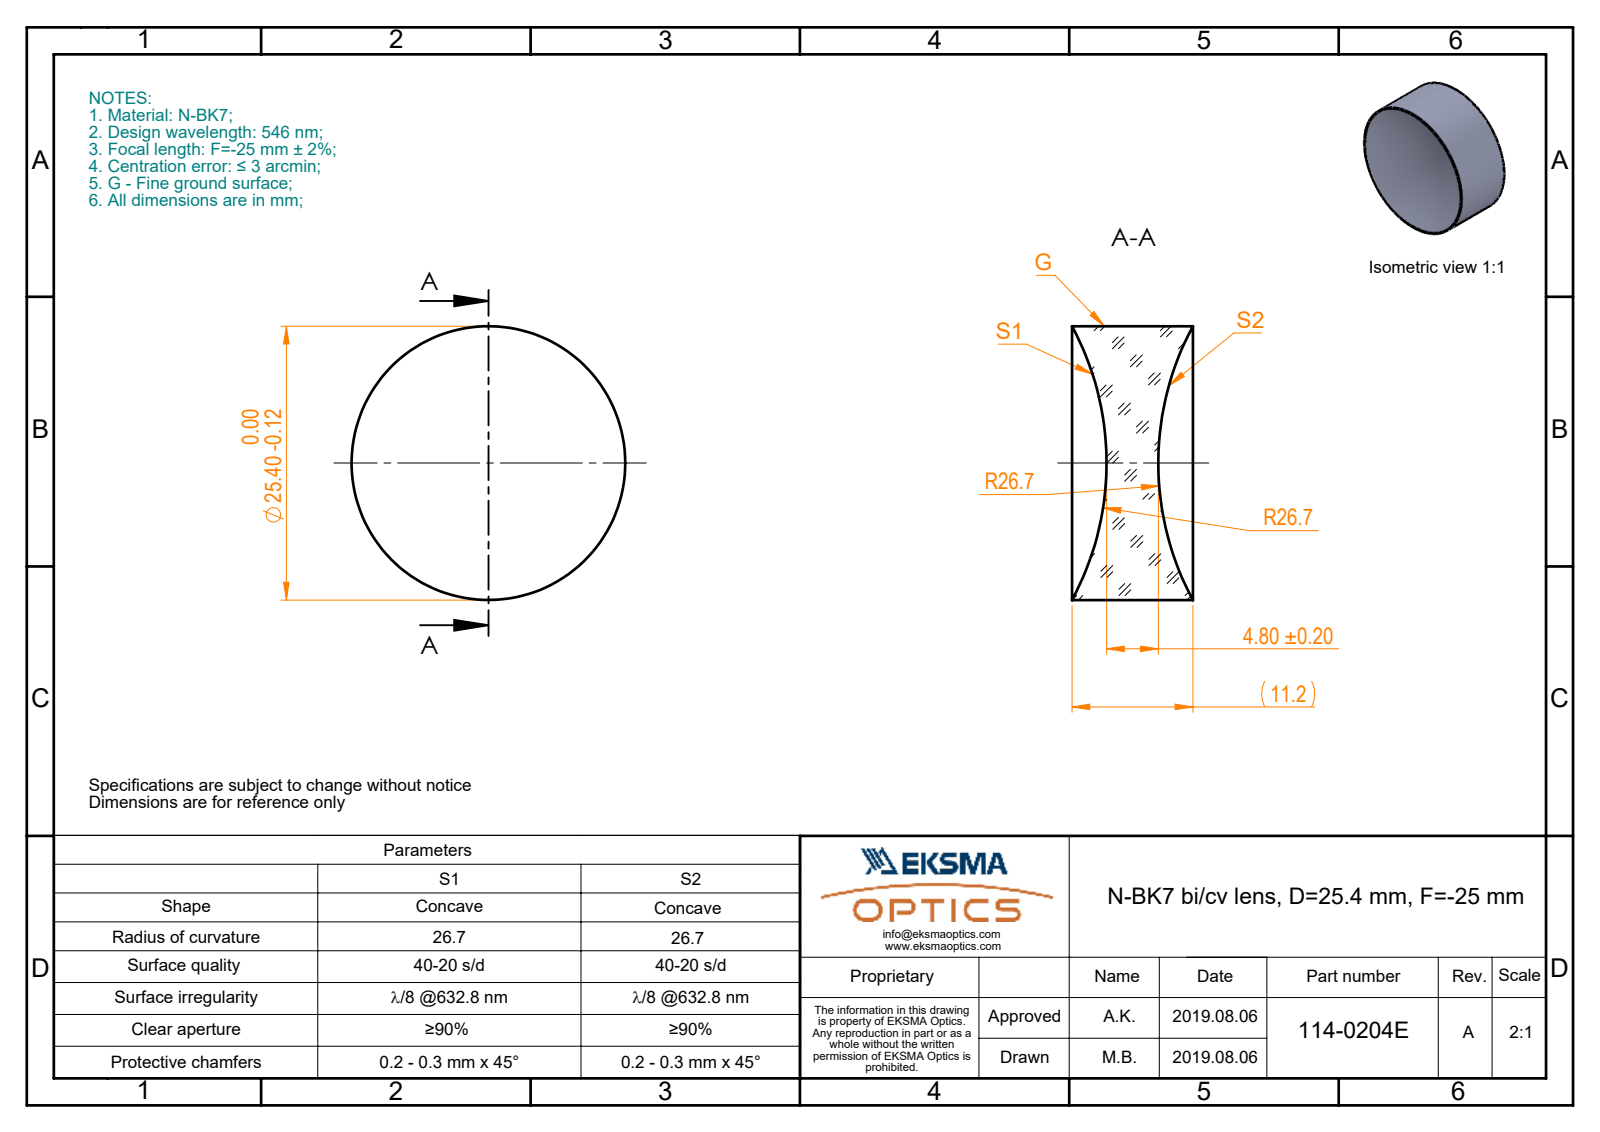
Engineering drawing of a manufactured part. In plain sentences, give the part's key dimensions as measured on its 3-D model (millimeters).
The part is named "114-0204E BK7 bi-cv 25.4 F-25". Its 3-D file was written by "SolidWorks 2017 (CONFIG_CONTROL_DESIGN)". It is 1 solid with 6 faces: 0 planar, 2 cylindrical and 4 other. Overall it measures 25.4 by 25.4 by 11.22 millimeters. Its volume is 4 024 cubic millimeters and its surface area 1 973 square millimeters. Round bosses or shafts: 1 of diameter 25.4.
